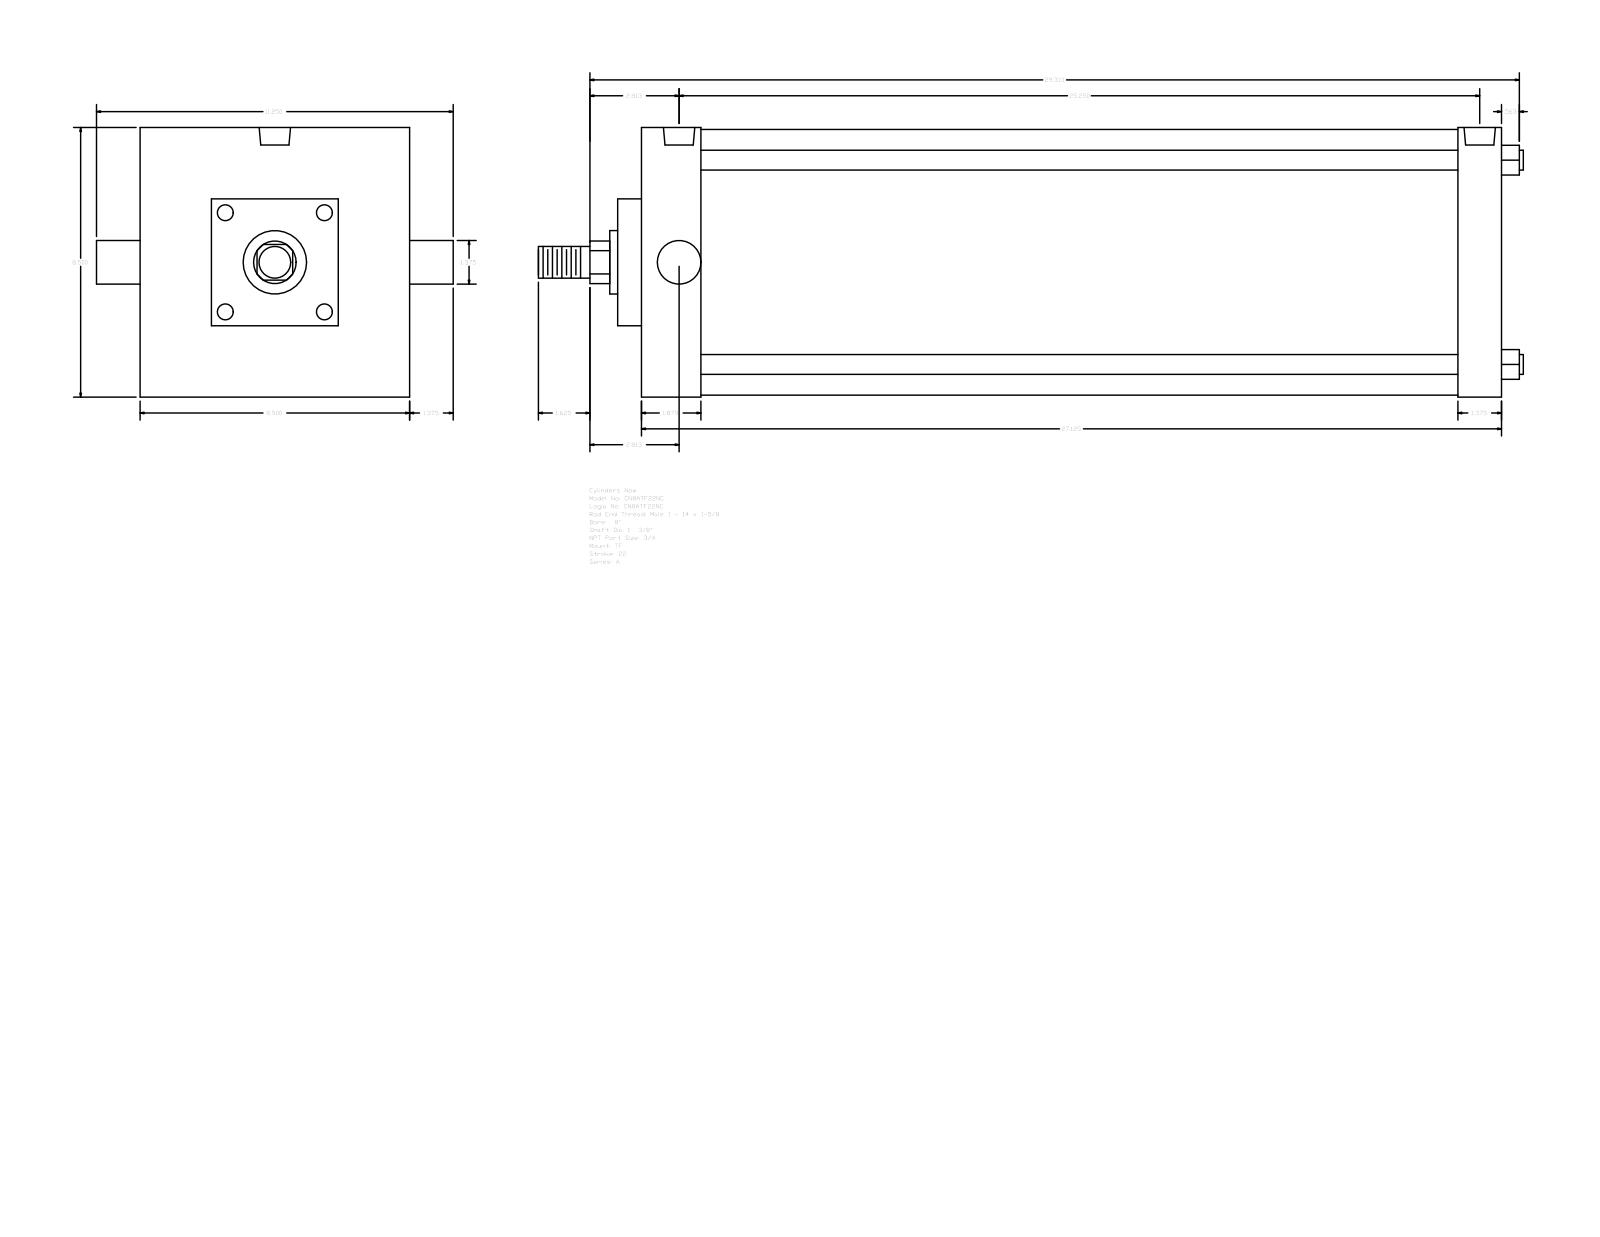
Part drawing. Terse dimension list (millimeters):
name: A_TF__0800_1.375
written by: GSSL Pune (CONFIG_CONTROL_DESIGN)
unit: mm
bodies: 0 solids, 89 faces (65 planar, 24 cylindrical, 0 other)
size: 788.99 × 285.75 × 215.9
holes: 3× ⌀15.08, 2× ⌀25.12
bosses: 4× ⌀15.88, 2× ⌀34.92, 1× ⌀212.72, 1× ⌀50.8, 1× ⌀25.4
rounds: 1× R17.06
face distances: 688.98, 215.9, 47.63, 641.35, 654.06, 606.43, 34.92, 19.04, 66.67, 673.1
hole spacings: 6.35, 635, 628.65, 641.35
